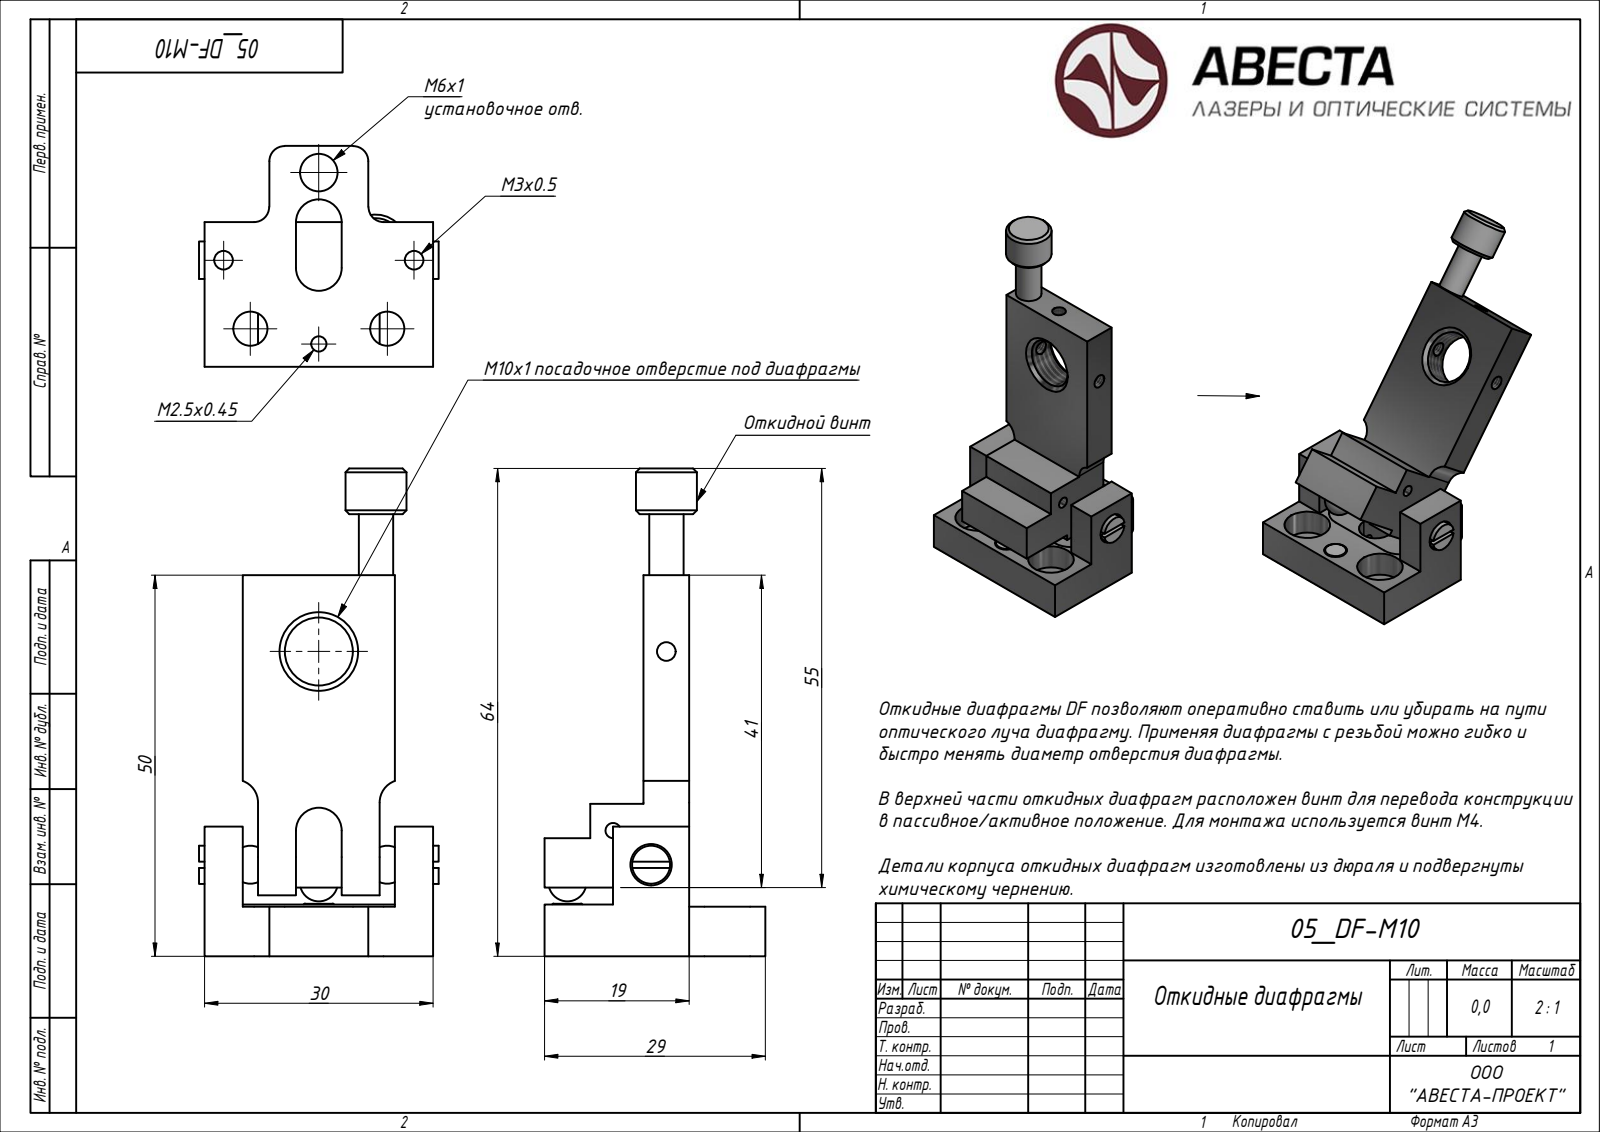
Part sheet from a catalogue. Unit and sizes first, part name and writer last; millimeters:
Units: millimetres
Overall size (bounding box): 64 × 31.46 × 29
Round holes (diameter × count): ⌀2.46 ×5, ⌀2 ×2, ⌀4.5 ×2, ⌀8 ×2, ⌀2.01 ×1, ⌀3 ×1, ⌀4 ×1, ⌀4.92 ×1, ⌀5 ×1, ⌀5.46 ×1, ⌀8.92 ×1
Round bosses / shafts (diameter × count): ⌀8 ×1, ⌀6 ×1, ⌀5 ×1, ⌀4.5 ×1, ⌀3 ×1
Partial cylindrical surfaces — rounded edges, fillets, slot ends (radius × count): R3 ×5, R2 ×4, R4 ×2, R5 ×1
Main face-to-face distances: 6, 7, 13, 5, 18, 2, 11, 9, 25, 20
Hole centre spacings: 9.22, 9.66, 12.66, 14.21, 16.65, 16.99, 22.39, 23.31
Volume: 10 252 mm³ · Surface area: 8 303 mm²
Bodies: 11 solids, 148 faces (67 planar, 52 cylindrical, 29 other)
Part name (STEP PRODUCT): 05_DF-M10; M01_Основание; M02_Откидушка; Пятка4х4 (+4 more)
STEP written by: Autodesk Inventor 2020 (CONFIG_CONTROL_DESIGN)
